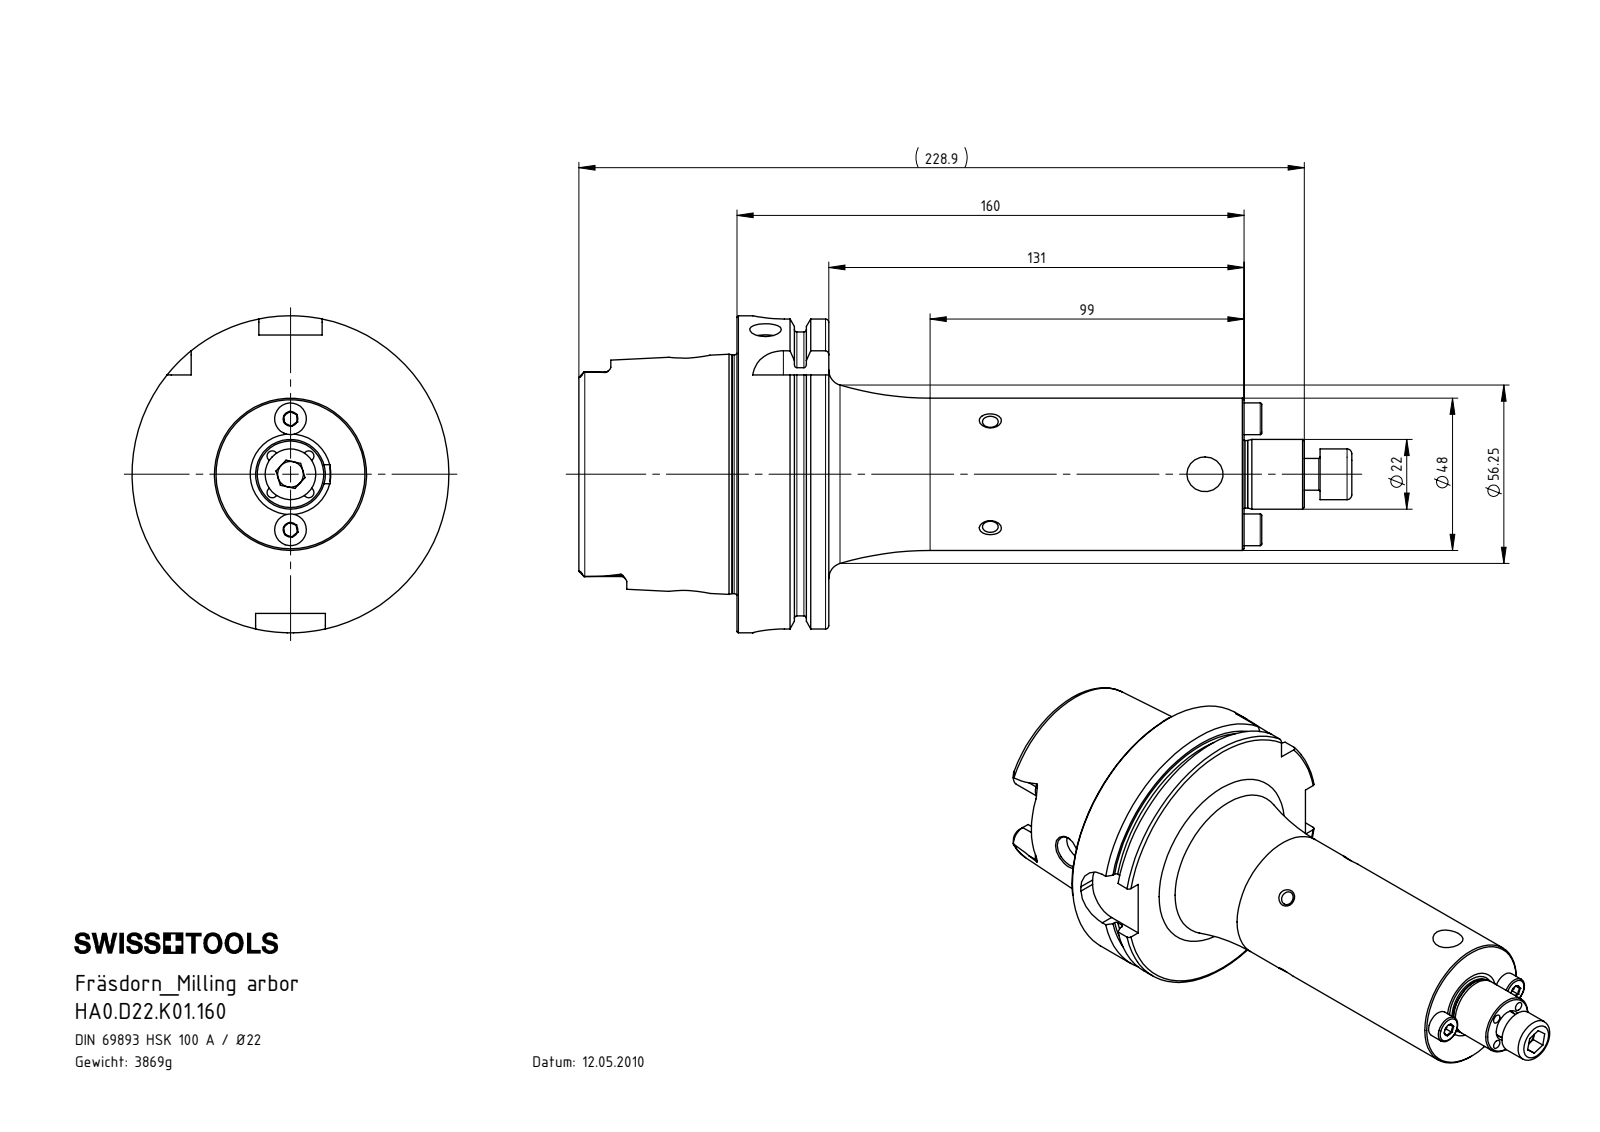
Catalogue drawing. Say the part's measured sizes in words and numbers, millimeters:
The part is named "HA0.D22.K01.160; D22-ER2.001.017_B; D22-ER1.002.025_A_Default; HA0-D22.K01.160_C_Fertigbearbeitung". Its 3-D file was written by "SolidWorks 2011 (AUTOMOTIVE_DESIGN)". It is 4 solids with 371 faces: 84 planar, 112 cylindrical and 175 other. Overall it measures 243.9 by 100 by 100 millimeters. Its volume is 492 618 cubic millimeters and its surface area 80 449 square millimeters. Round holes: 4 of diameter 5, 3 of diameter 3.3, 3 of diameter 10, 2 of diameter 4.2, 2 of diameter 8, 2 of diameter 12, 1 of diameter 8.5, 1 of diameter 10.5, 1 of diameter 22.5, 1 of diameter 26, 1 of diameter 53, 1 of diameter 63. Round bosses or shafts: 3 of diameter 10, 2 of diameter 5, 2 of diameter 3.8, 1 of diameter 100, 1 of diameter 91.95, 1 of diameter 75.26, 1 of diameter 48, 1 of diameter 22. Partial cylindrical surfaces (rounded edges, fillets, slot ends): 6 of radius 1.9, 4 of radius 4.88, 4 of radius 10, 2 of radius 3. The main face-to-face distances are 28.95, 16.5, 12.45, 160, 147.55, 131.05, 49.9, 62.35, 78.85, 209.9. The hole center spacings are 8.13, 13.08, 17.5, 23.95, 71.05, 16.26, 35.
